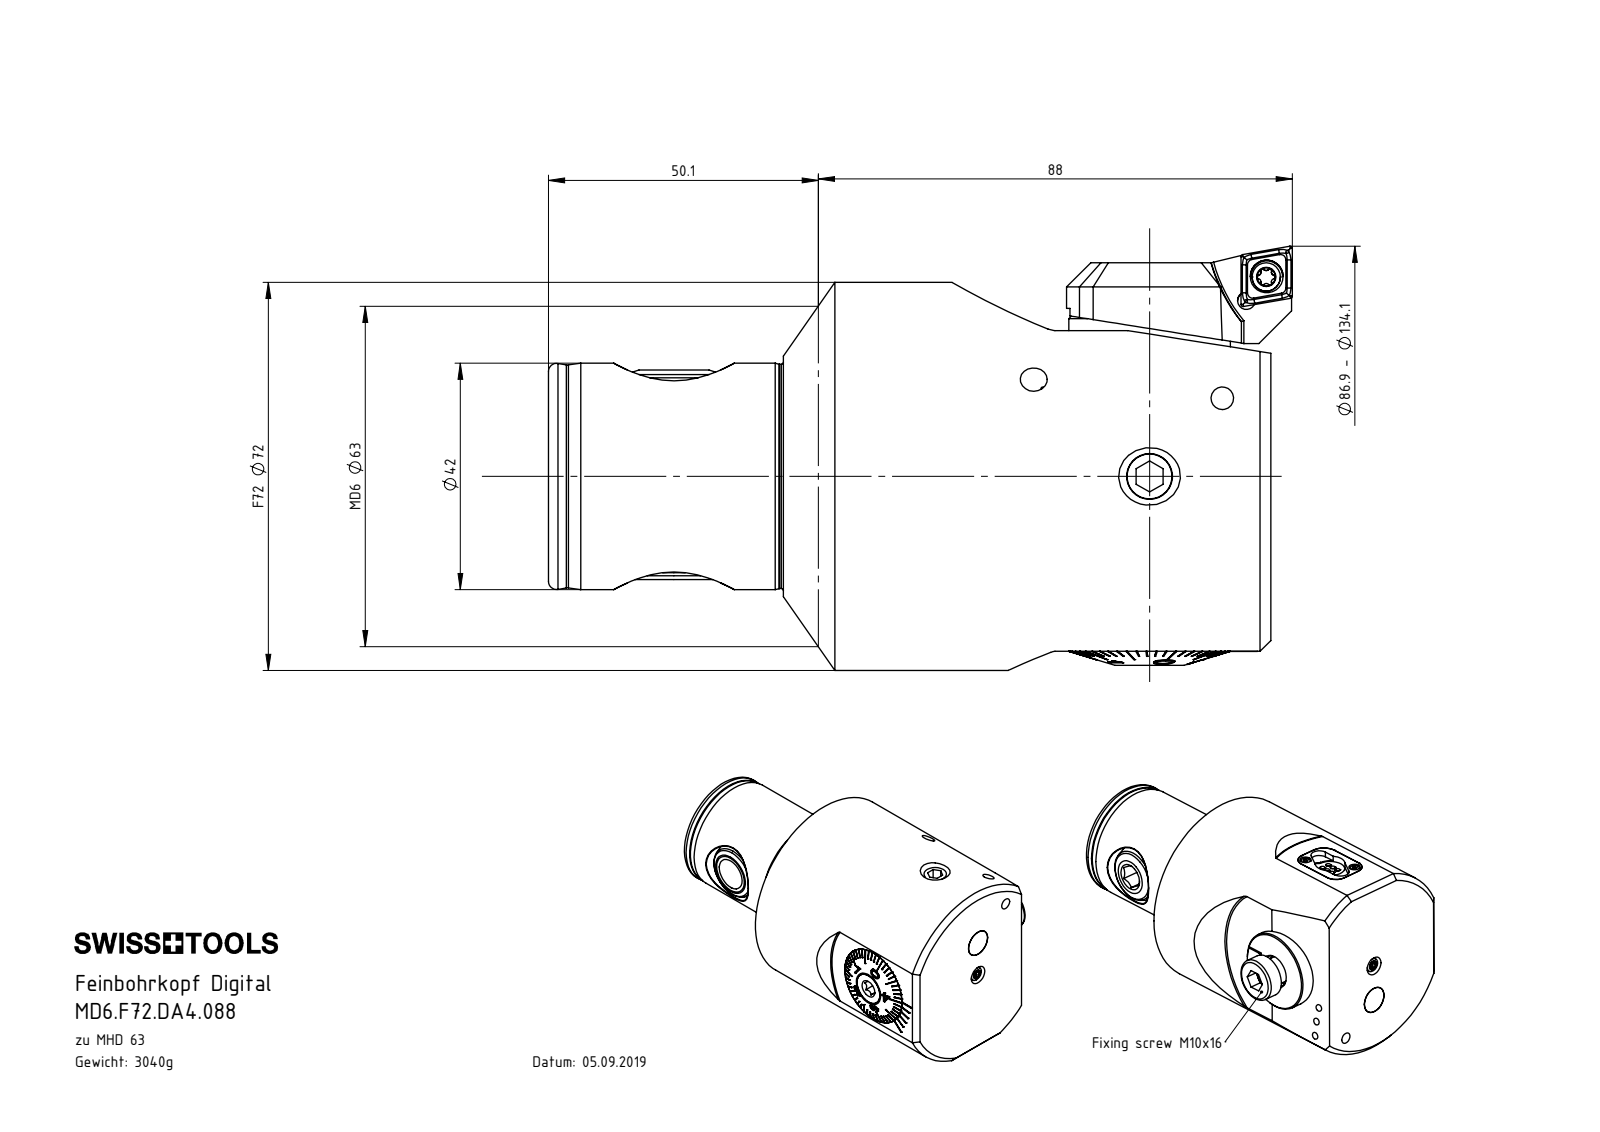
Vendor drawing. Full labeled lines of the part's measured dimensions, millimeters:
Part name (STEP PRODUCT): F72-BG1.DA3.030_A; ISO 4762 - M2 x 4; WCB-ER2.001.009_A; ISO 4026 - M10 x 16 (+8 more)
STEP written by: SolidWorks 2017 (CONFIG_CONTROL_DESIGN)
Units: millimetres
Bodies: 41 solids, 1271 faces (542 planar, 295 cylindrical, 434 other)
Overall size (bounding box): 138.08 × 78.7 × 72
Volume: 391 104 mm³ · Surface area: 78 556 mm²
Round holes (diameter × count): ⌀4.2 ×5, ⌀3.3 ×4, ⌀2.5 ×3, ⌀8.5 ×3, ⌀1.6 ×2, ⌀2.2 ×2, ⌀5 ×2, ⌀8 ×2, ⌀12 ×2, ⌀12.5 ×2, ⌀13 ×2, ⌀4.4 ×1
Round bosses / shafts (diameter × count): ⌀1.9 ×6, ⌀10 ×2, ⌀5.25 ×2, ⌀4 ×2, ⌀3.8 ×2, ⌀2 ×2, ⌀72 ×1, ⌀42 ×1
Partial cylindrical surfaces — rounded edges, fillets, slot ends (radius × count): R0.34 ×12, R0.59 ×12, R1.1 ×6, R1.2 ×6, R2 ×6, R2.5 ×6, R0.5 ×5, R3.2 ×3
Main face-to-face distances: 134.08, 53.01, 2.5, 4, 12.59, 65.6, 72.1, 59.51, 6.5, 2.6
Hole centre spacings: 9.52, 1.21, 5.73, 5.87, 8.49, 10.59, 14.5, 17.97
